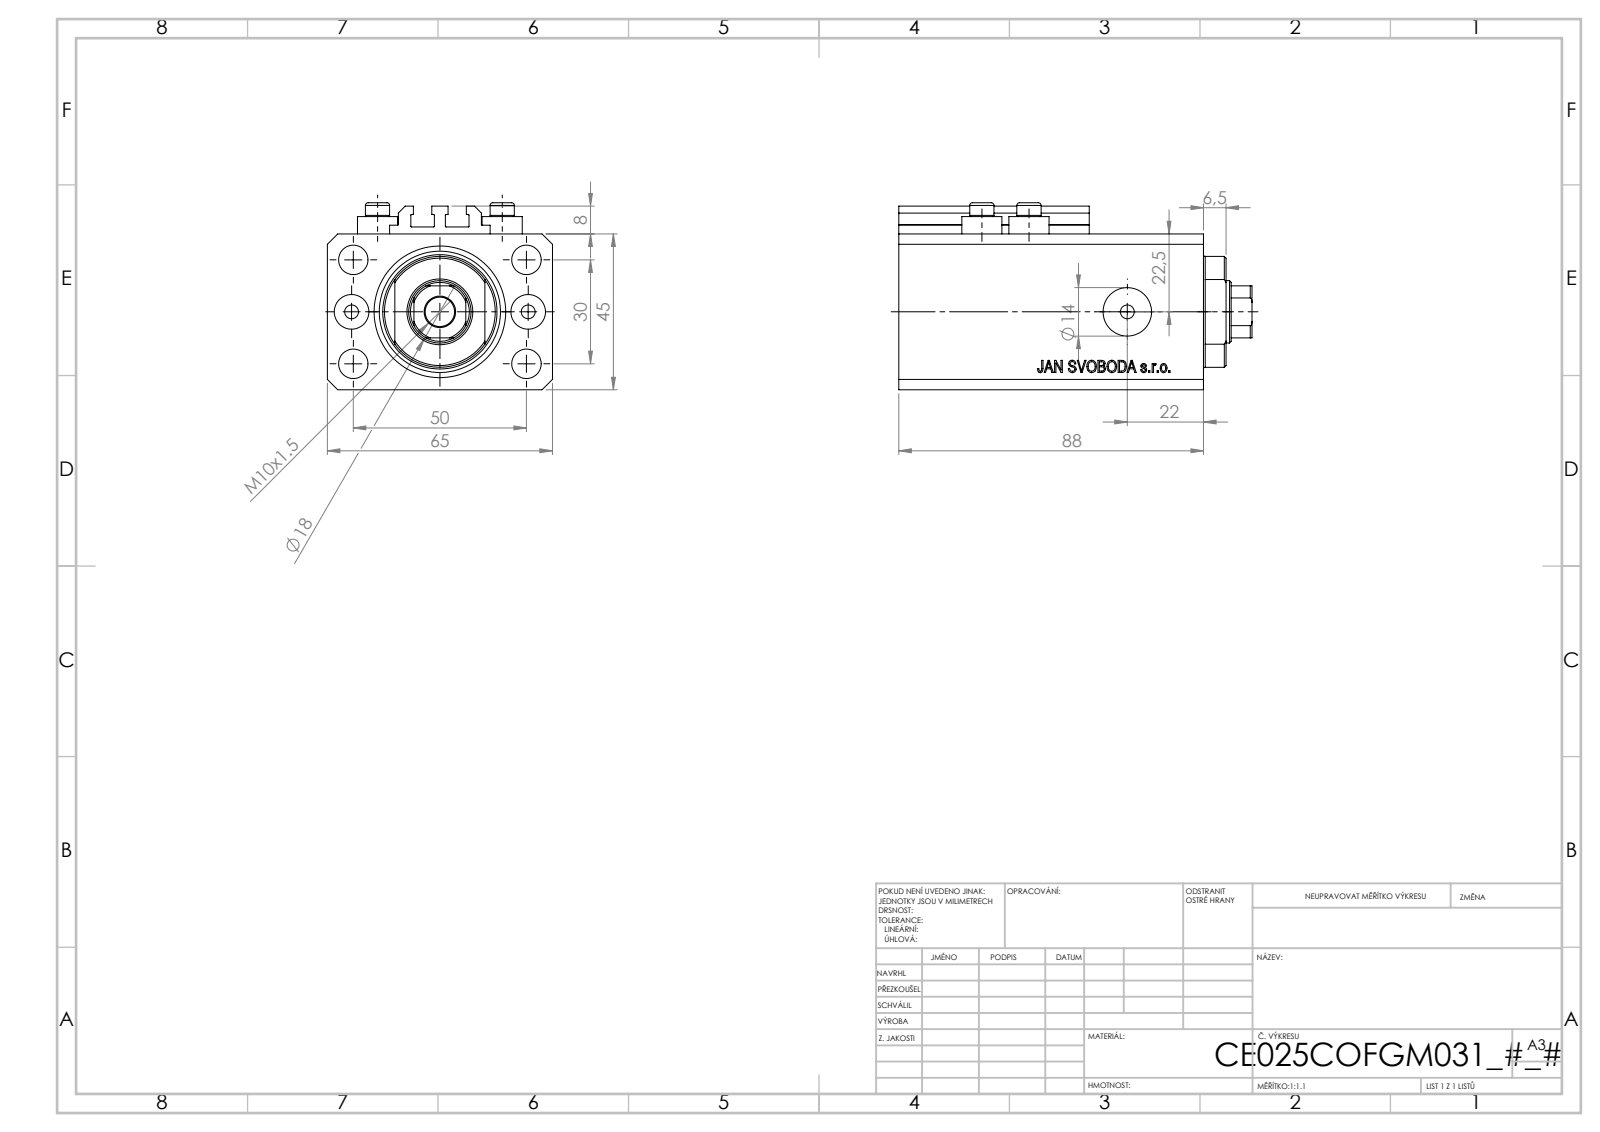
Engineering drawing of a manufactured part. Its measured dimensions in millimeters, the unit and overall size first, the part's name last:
Units: millimetres
Overall size (bounding box): 102 × 65 × 54
Round holes (diameter × count): ⌀4 ×8, ⌀8.5 ×5, ⌀10 ×2, ⌀14 ×2, ⌀18 ×1, ⌀25 ×1, ⌀38 ×1
Round bosses / shafts (diameter × count): ⌀11.6 ×4, ⌀7 ×4
Partial cylindrical surfaces — rounded edges, fillets, slot ends (radius × count): R0.2 ×10, R8.5 ×1, R16 ×1
Main face-to-face distances: 45, 65, 14, 74, 88, 47, 6.9, 67.1, 81.1, 3
Hole centre spacings: 15.01, 29.15, 52.68, 13.6, 25.5, 30, 36, 38.48
Volume: 240 207 mm³ · Surface area: 63 378 mm²
Bodies: 8 solids, 1034 faces (504 planar, 86 cylindrical, 444 other)
Part name (STEP PRODUCT): V250CE_C_Body; ALLEN BOLT V250CE; V250CE_C_VCP; V250CE_VC_C
STEP written by: SolidWorks 2019 (CONFIG_CONTROL_DESIGN)
